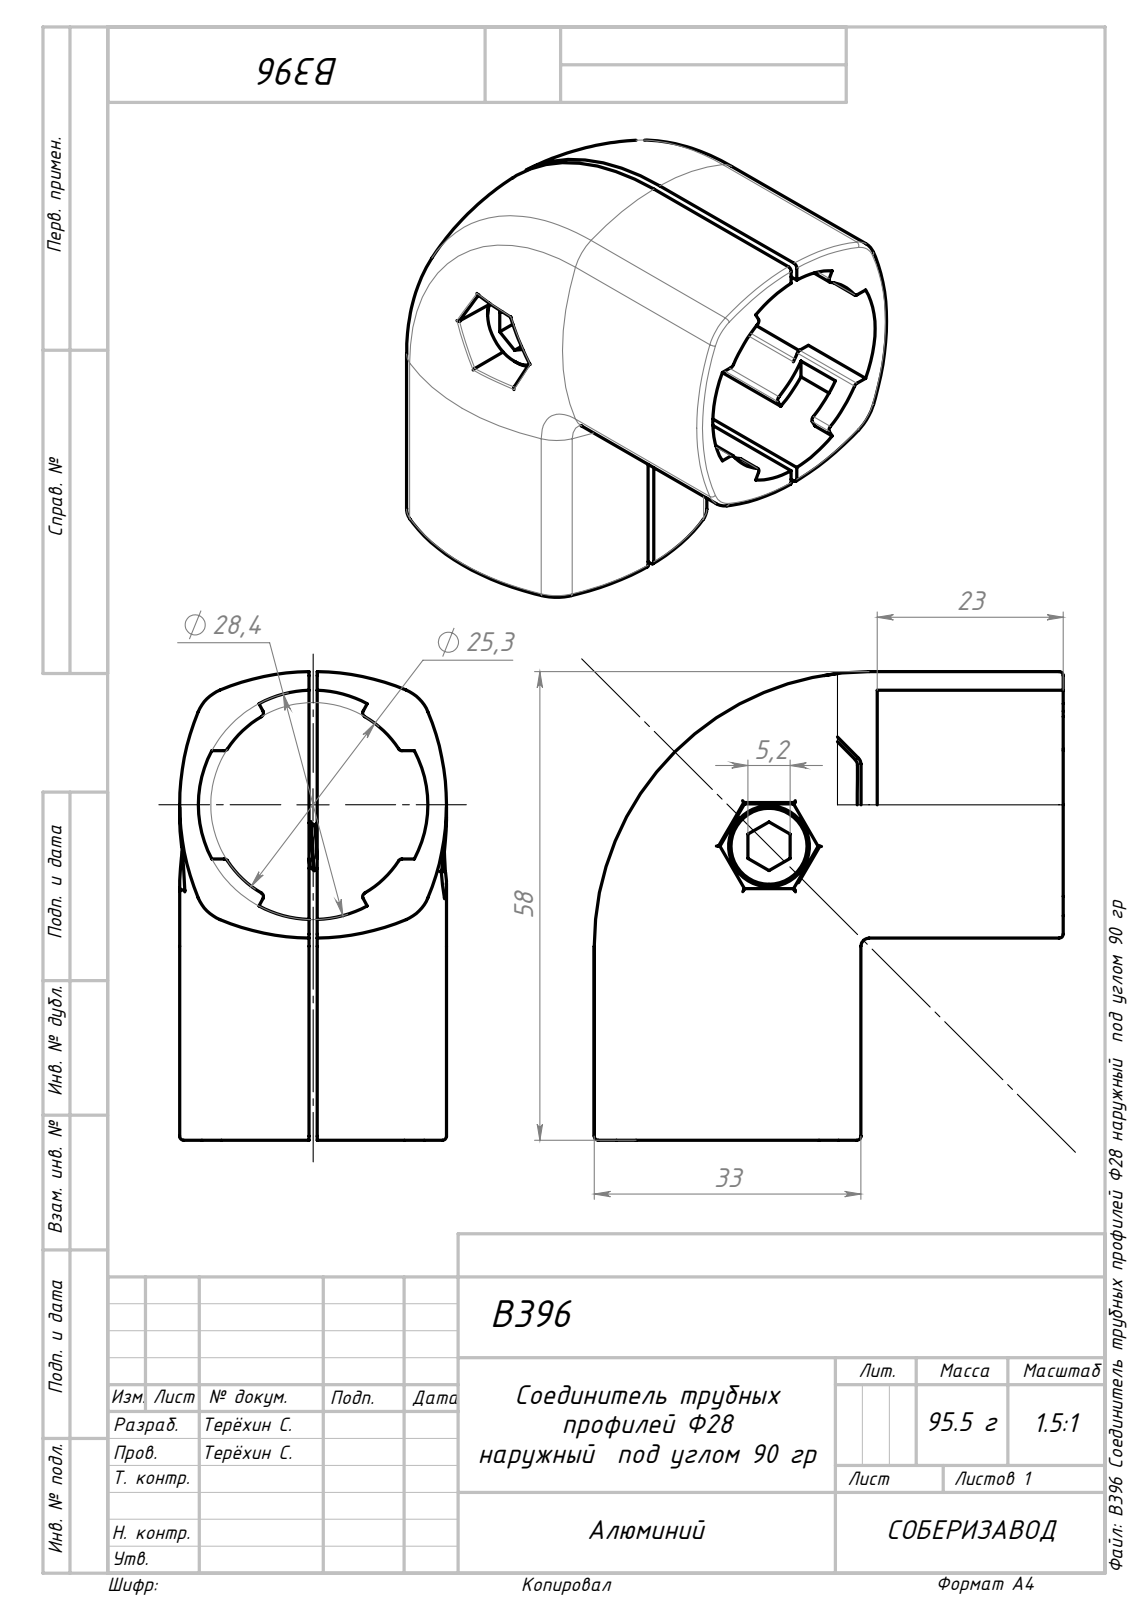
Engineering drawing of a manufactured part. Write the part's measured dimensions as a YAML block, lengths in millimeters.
part_name: "B396 Соединитель трубных профилей Ф28 наружный под углом 90 гр"
step_written_by: "SolidWorks 2022 (AUTOMOTIVE_DESIGN)"
units: millimeters
bodies: {solids: 4, faces: 393, planar: 126, cylindrical: 136, other: 131}
overall_size: [58, 58, 33]
volume: 32918
surface_area: 21857
round_holes:
  - {diameter: 28.4, count: 2}
  - {diameter: 5.2, count: 1}
  - {diameter: 6.5, count: 1}
round_bosses_or_shafts:
  - {diameter: 10, count: 1}
  - {diameter: 6, count: 1}
partial_cylinders:
  - {radius: 0.5, count: 24}
  - {radius: 1, count: 8}
  - {radius: 5, count: 8}
  - {radius: 30, count: 8}
  - {radius: 12.65, count: 2}
face_to_face_distances: [1, 23, 6, 7, 13, 12, 31.11, 14, 5, 10]
